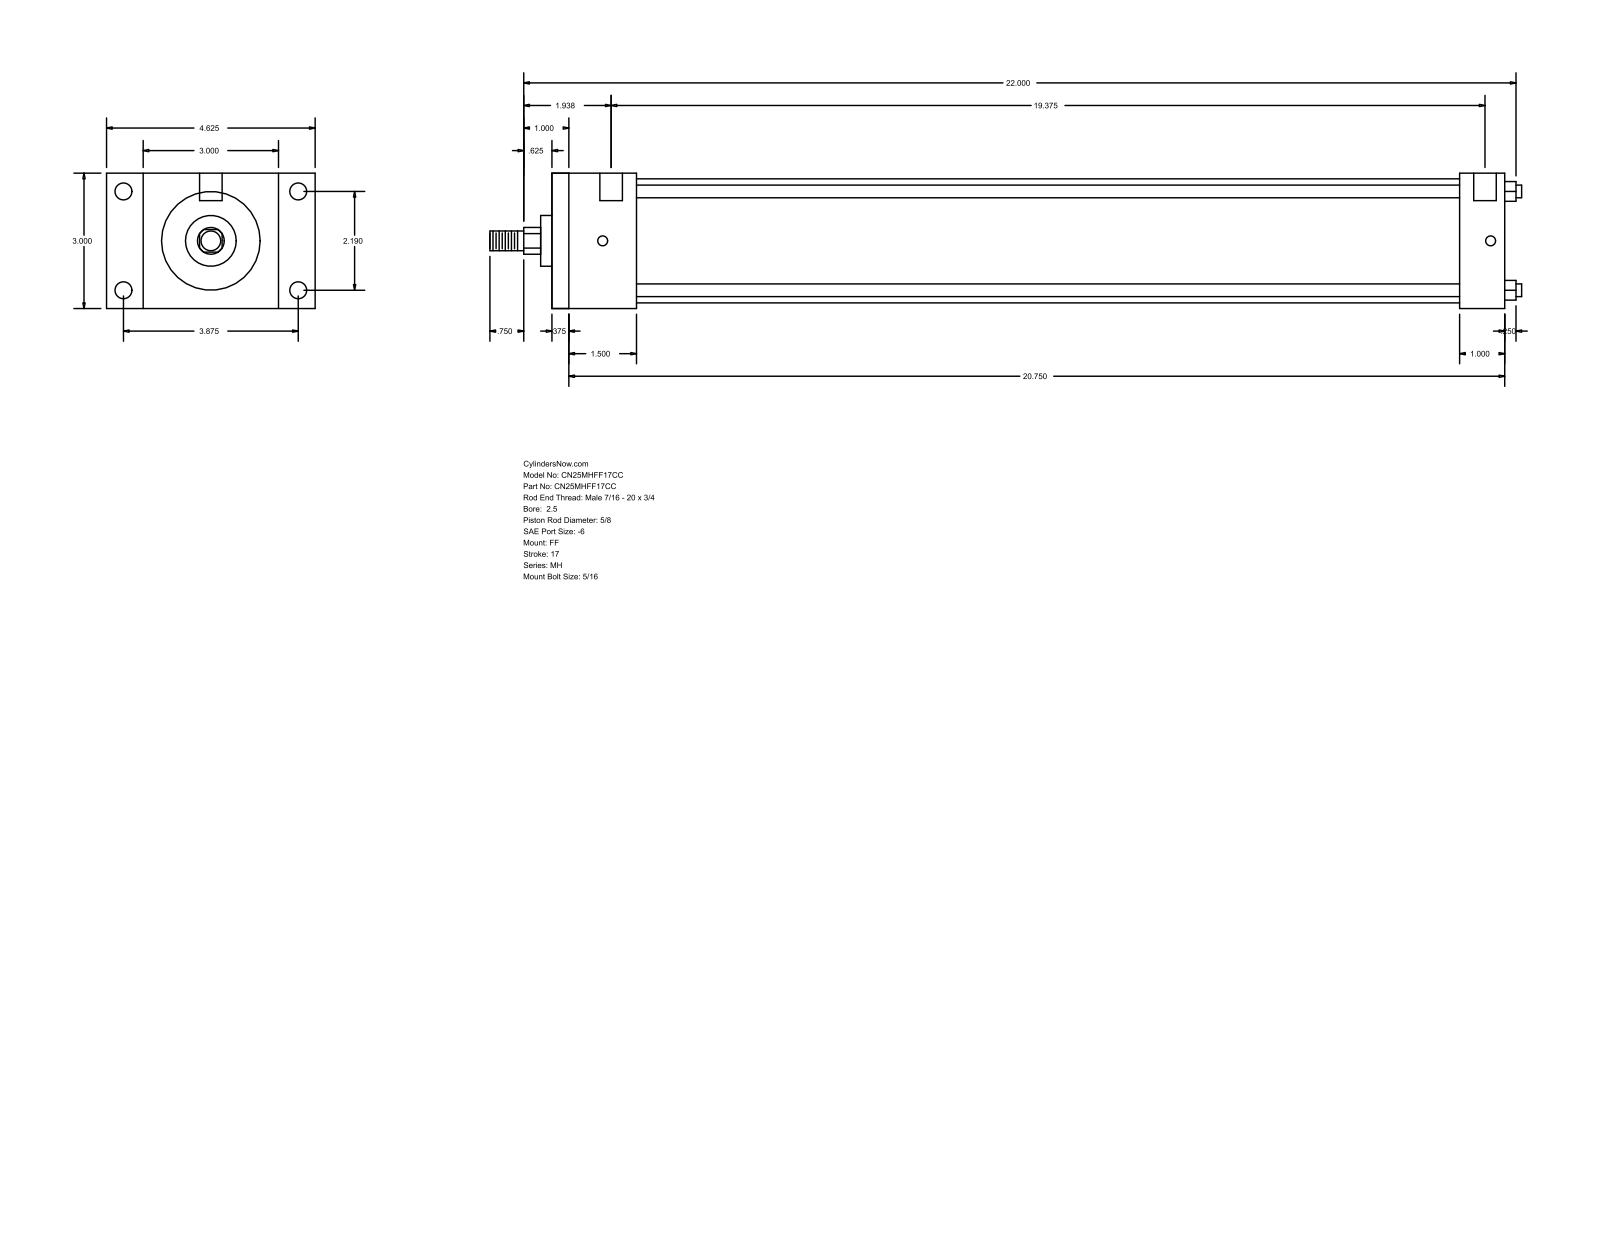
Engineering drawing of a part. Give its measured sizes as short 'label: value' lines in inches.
name: MH_FF__0250_0.625
written by: GSSL Pune (CONFIG_CONTROL_DESIGN)
unit: in
bodies: 0 solids, 92 faces (64 planar, 28 cylindrical, 0 other)
size: 22.875 × 4.625 × 3
holes: 4× ⌀0.219, 4× ⌀0.375, 2× ⌀0.5
bosses: 4× ⌀0.281, 1× ⌀2.75, 1× ⌀1.125, 1× ⌀0.625, 1× ⌀0.437
rounds: 1× R0.297
face distances: 3, 21.125, 20.75, 0.375, 1, 1.875, 20.125, 1.5, 19.75, 18.25
hole spacings: 2.19, 3.875, 4.451, 19.687, 0.125, 0.187, 19.375, 19.5
